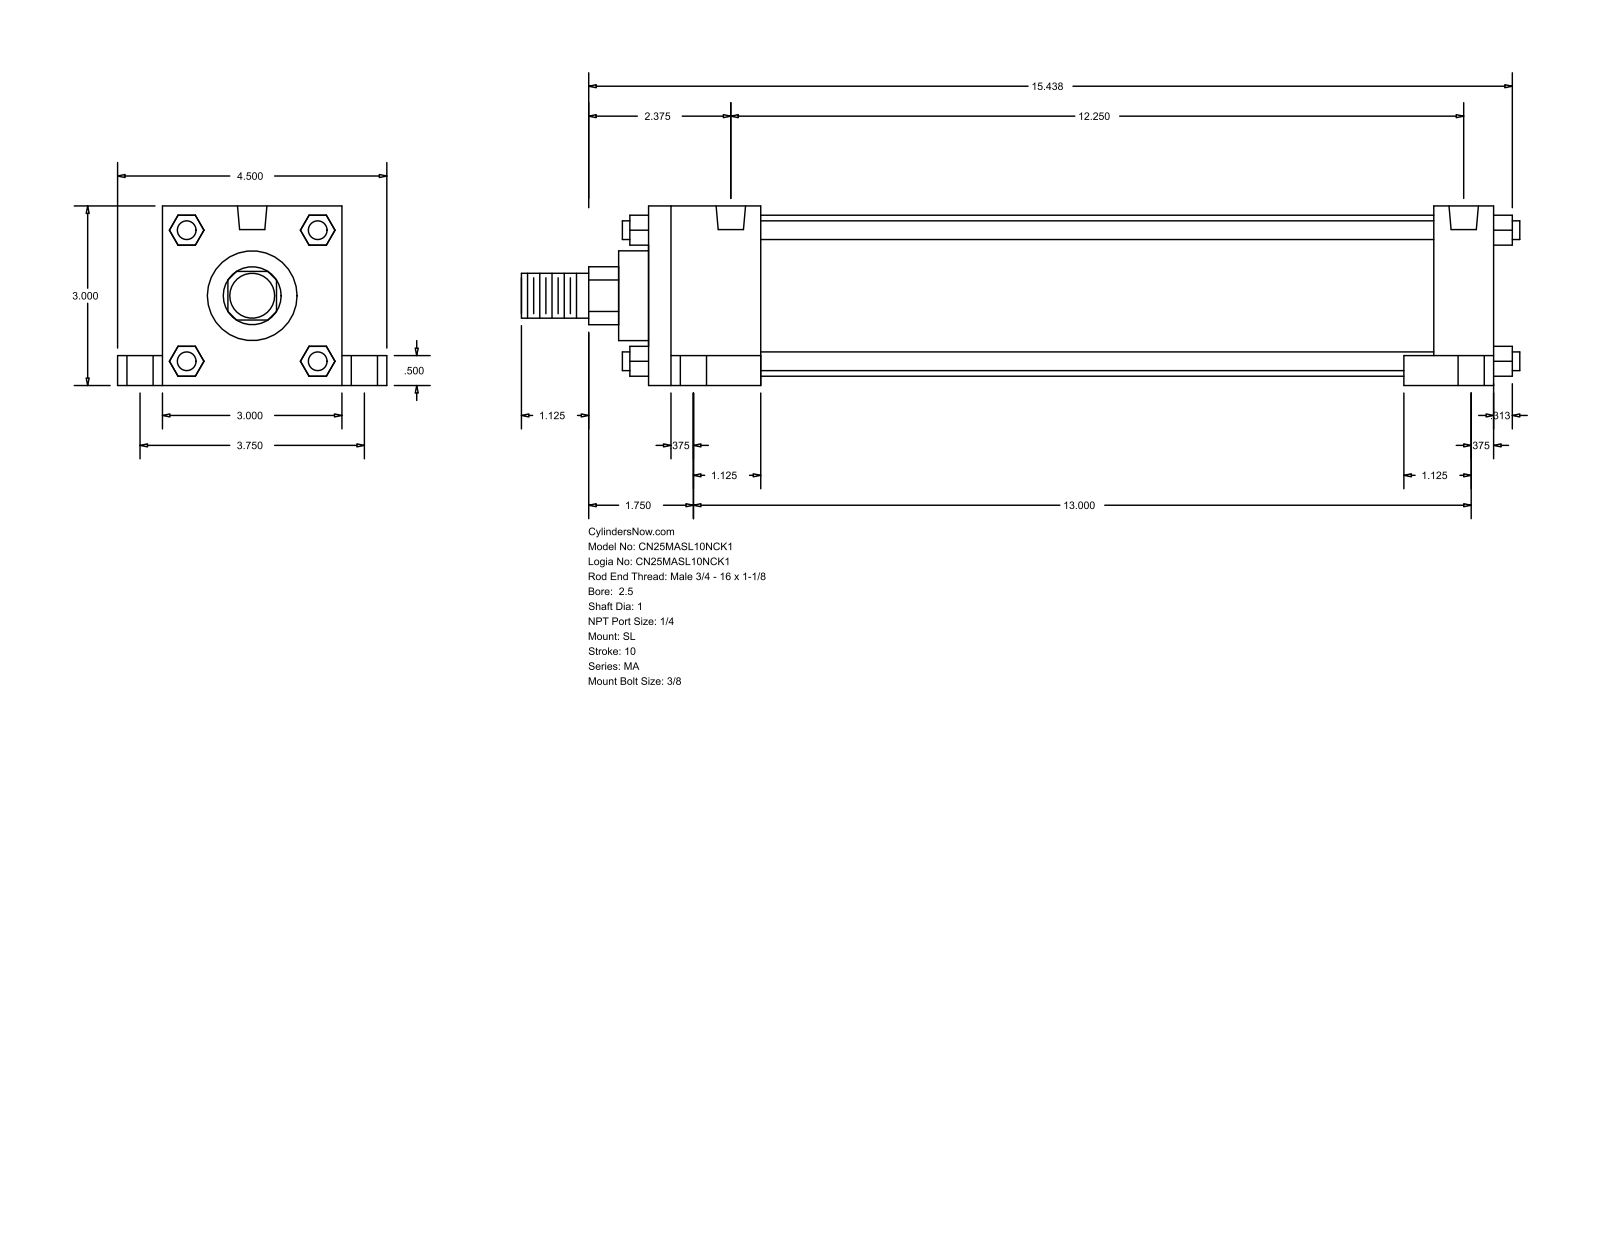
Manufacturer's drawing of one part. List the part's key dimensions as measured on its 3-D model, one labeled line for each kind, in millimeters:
Part name (STEP PRODUCT): MA_SL__0250_1
STEP written by: GSSL Pune (CONFIG_CONTROL_DESIGN)
Units: millimetres
Bodies: 0 solids, 148 faces (112 planar, 36 cylindrical, 0 other)
Overall size (bounding box): 423.86 × 114.3 × 76.2
Round holes (diameter × count): ⌀7.94 ×4, ⌀11.11 ×4, ⌀17.46 ×4, ⌀12.49 ×2
Round bosses / shafts (diameter × count): ⌀7.94 ×4, ⌀68.33 ×1, ⌀38.1 ×1, ⌀25.4 ×1, ⌀19.05 ×1
Partial cylindrical surfaces — rounded edges, fillets, slot ends (radius × count): R12.29 ×1
Main face-to-face distances: 76.2, 358.78, 12.7, 47.63, 311.15, 333.37, 285.74, 25.41, 19.05, 95.25
Hole centre spacings: 47.73, 50.2, 95.24, 311.15, 317.91, 330.2, 330.48, 343.66
